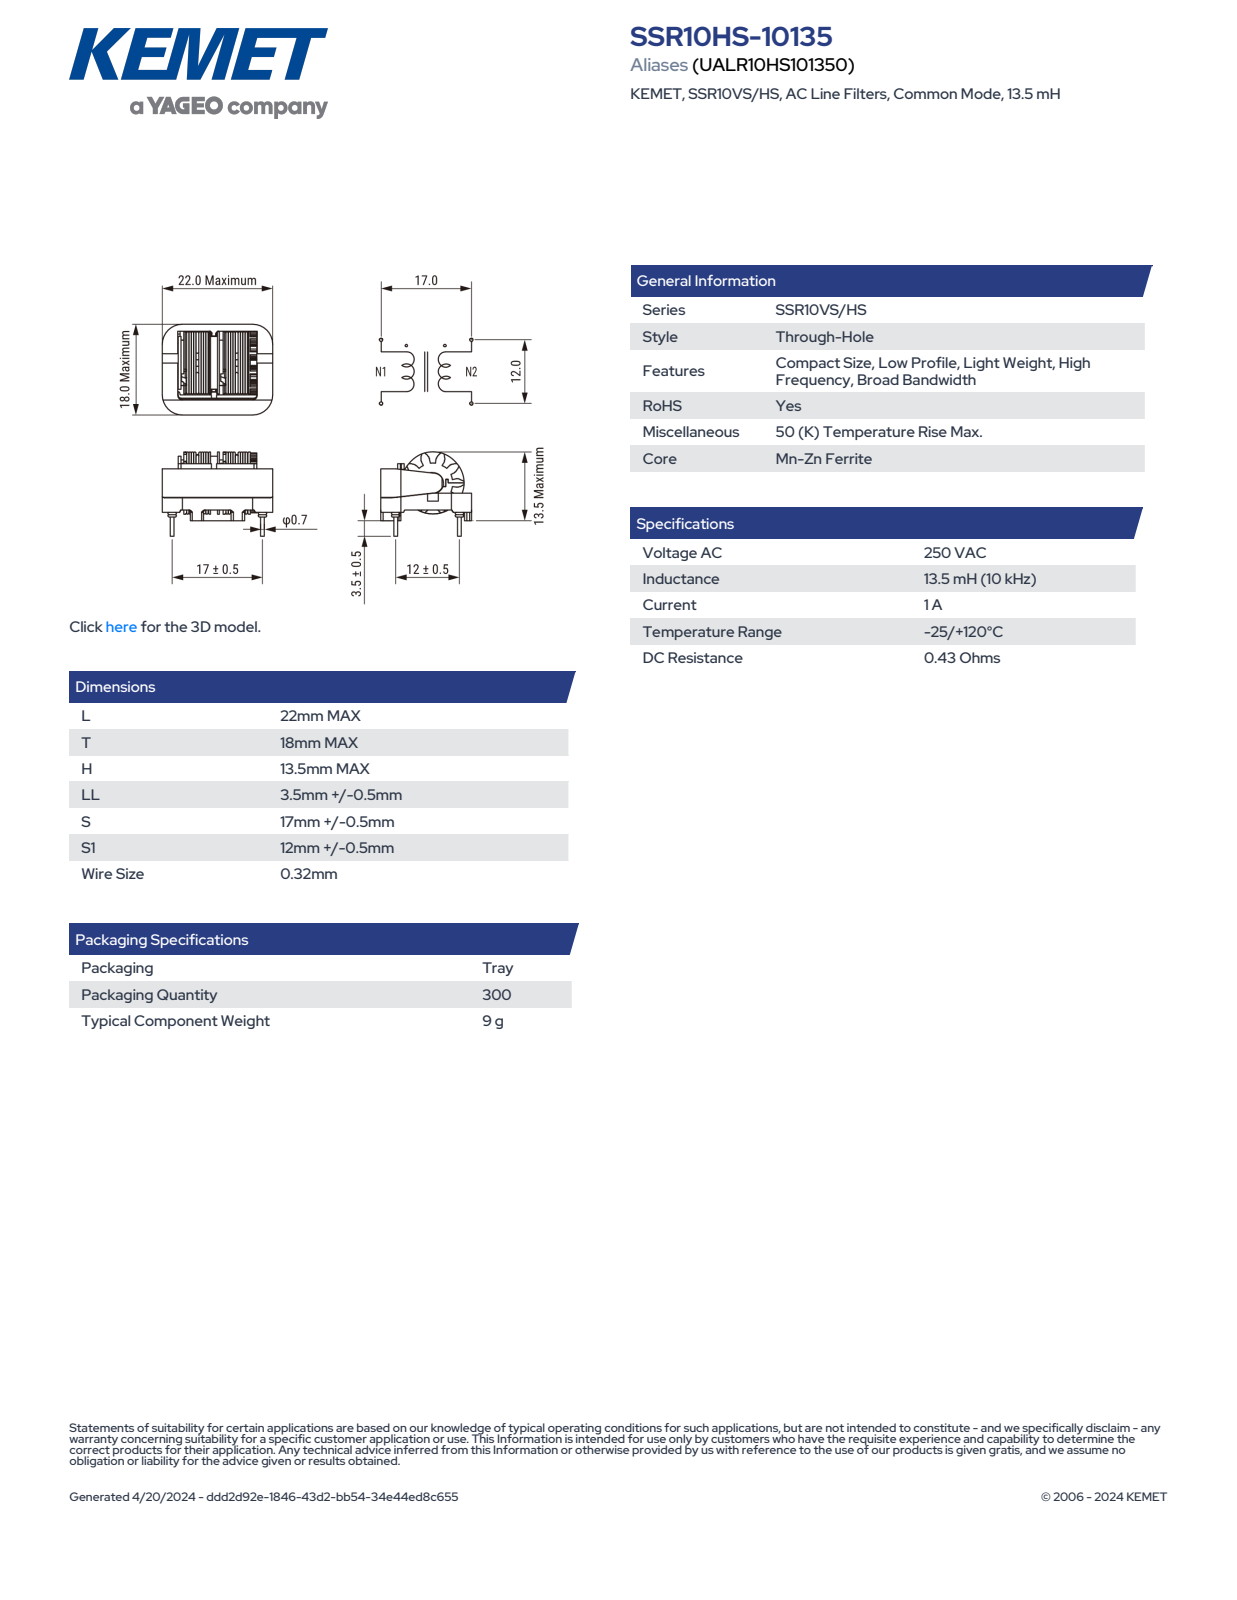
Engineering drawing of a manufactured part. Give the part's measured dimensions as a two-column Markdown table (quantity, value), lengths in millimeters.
| quantity | value |
| --- | --- |
| part name | SSR10HS(MAX-LOGO) |
| STEP written by | SolidWorks 2018 (AUTOMOTIVE_DESIGN) |
| units | millimeters |
| bodies | 1 solid, 424 faces (243 planar, 145 cylindrical, 36 other) |
| overall size | 22 × 18 × 17 |
| volume | 2 580 mm³ |
| surface area | 3 258 mm² |
| round holes (diameter × count) | 4 × 1 |
| round bosses / shafts (diameter × count) | 0.7 × 4, 11.7 × 1, 10 × 1, 8.6 × 1 |
| partial cylindrical surfaces (radius × count) | 0.5 × 23, 1.46 × 20, 0.4 × 8, 0.1 × 6, 3.8 × 6, 1 × 3, 0.2 × 2, 0.15 × 1 |
| main face-to-face distances | 7.4, 2.3, 3.5, 0.4, 0.5, 2.8, 0.6, 12, 11.5, 9.7 |
